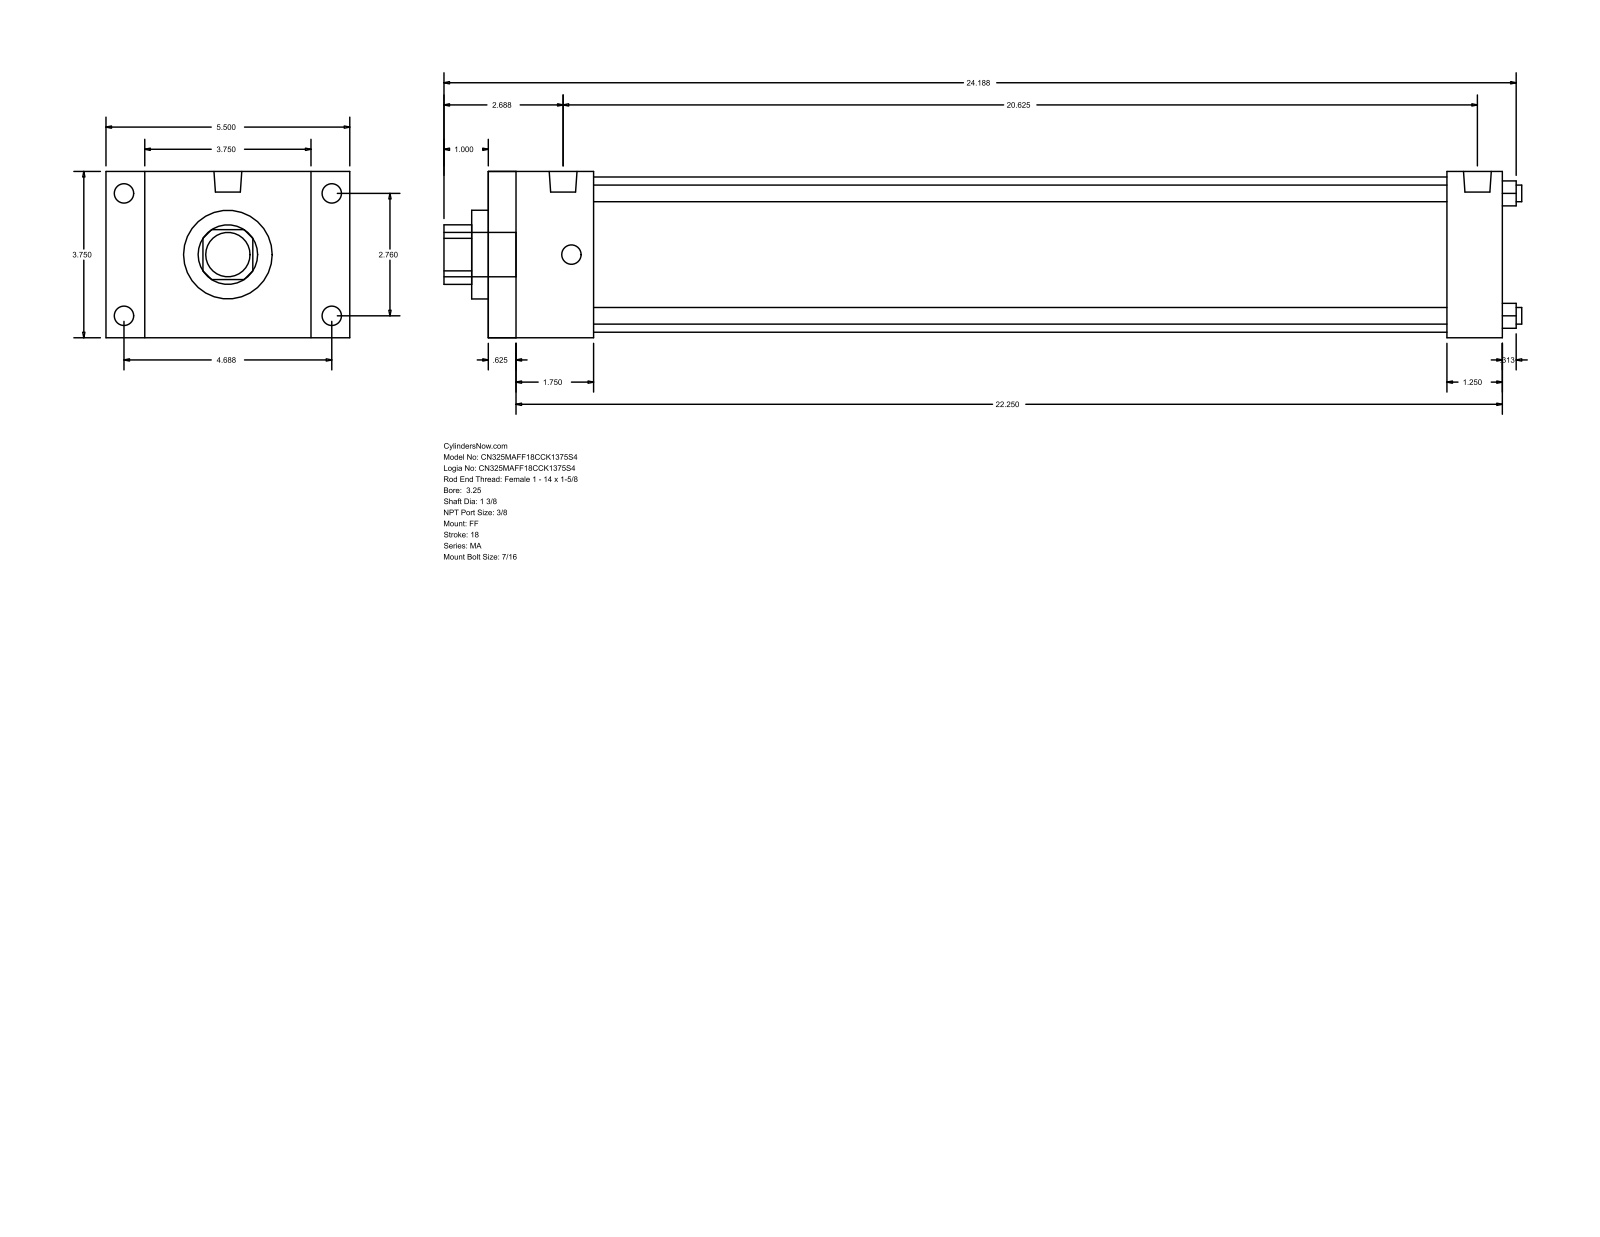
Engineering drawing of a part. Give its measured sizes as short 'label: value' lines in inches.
name: MA_FF__0325_1.375
written by: GSSL Pune (CONFIG_CONTROL_DESIGN)
unit: in
bodies: 0 solids, 92 faces (64 planar, 28 cylindrical, 0 other)
size: 24.313 × 5.5 × 3.75
holes: 4× ⌀0.375, 1× ⌀1.375, 1× ⌀2, 1× ⌀3.5
bosses: 8× ⌀0.437, 2× ⌀0.627, 1× ⌀1
rounds: 1× R0.672
face distances: 3.75, 22.875, 0.625, 22.25, 0.875, 4.625, 2.375, 21.625, 1.75, 21
hole spacings: 1.952, 2.76, 3.903
